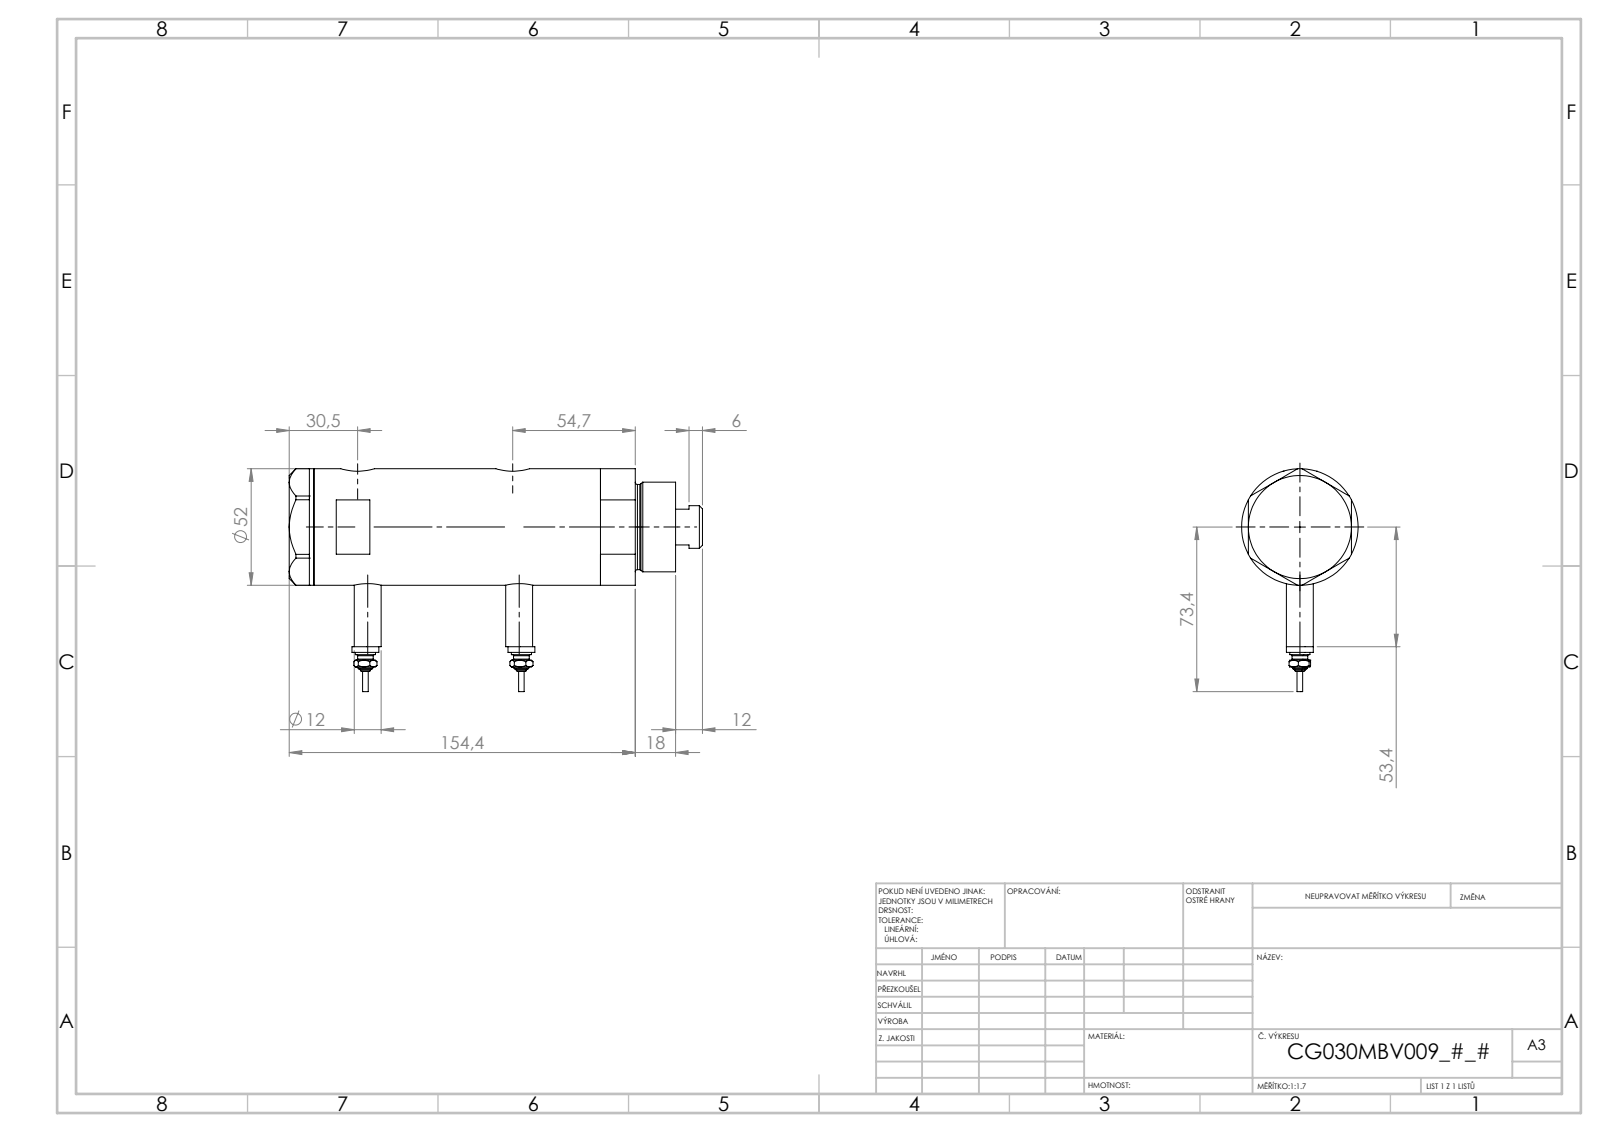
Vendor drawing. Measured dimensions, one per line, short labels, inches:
name: V270CG_VC; V270CG_MIDDLE; Switch; V270CG_BACK (+1 more)
written by: SolidWorks 2019 (CONFIG_CONTROL_DESIGN)
unit: in
bodies: 6 solids, 226 faces (93 planar, 69 cylindrical, 64 other)
size: 7.26 × 3.913 × 2.047
volume: 21.31 in³; area: 124.9 in²
holes: 2× ⌀0.383, 2× ⌀0.492, 2× ⌀0.591, 1× ⌀0.256, 1× ⌀0.787, 1× ⌀0.846, 1× ⌀1.181, 1× ⌀1.299, 1× ⌀1.732
bosses: 4× ⌀0.472, 2× ⌀0.354, 2× ⌀0.276, 2× ⌀0.177, 2× ⌀0.098, 1× ⌀2.047, 1× ⌀1.575, 1× ⌀1.496
face distances: 3.602, 0.937, 2.665, 0.433, 1.37, 4.035, 1.811, 1.433, 5.469, 5.035
hole spacings: 0.114, 0.177, 2.547, 2.661, 2.724, 2.839
